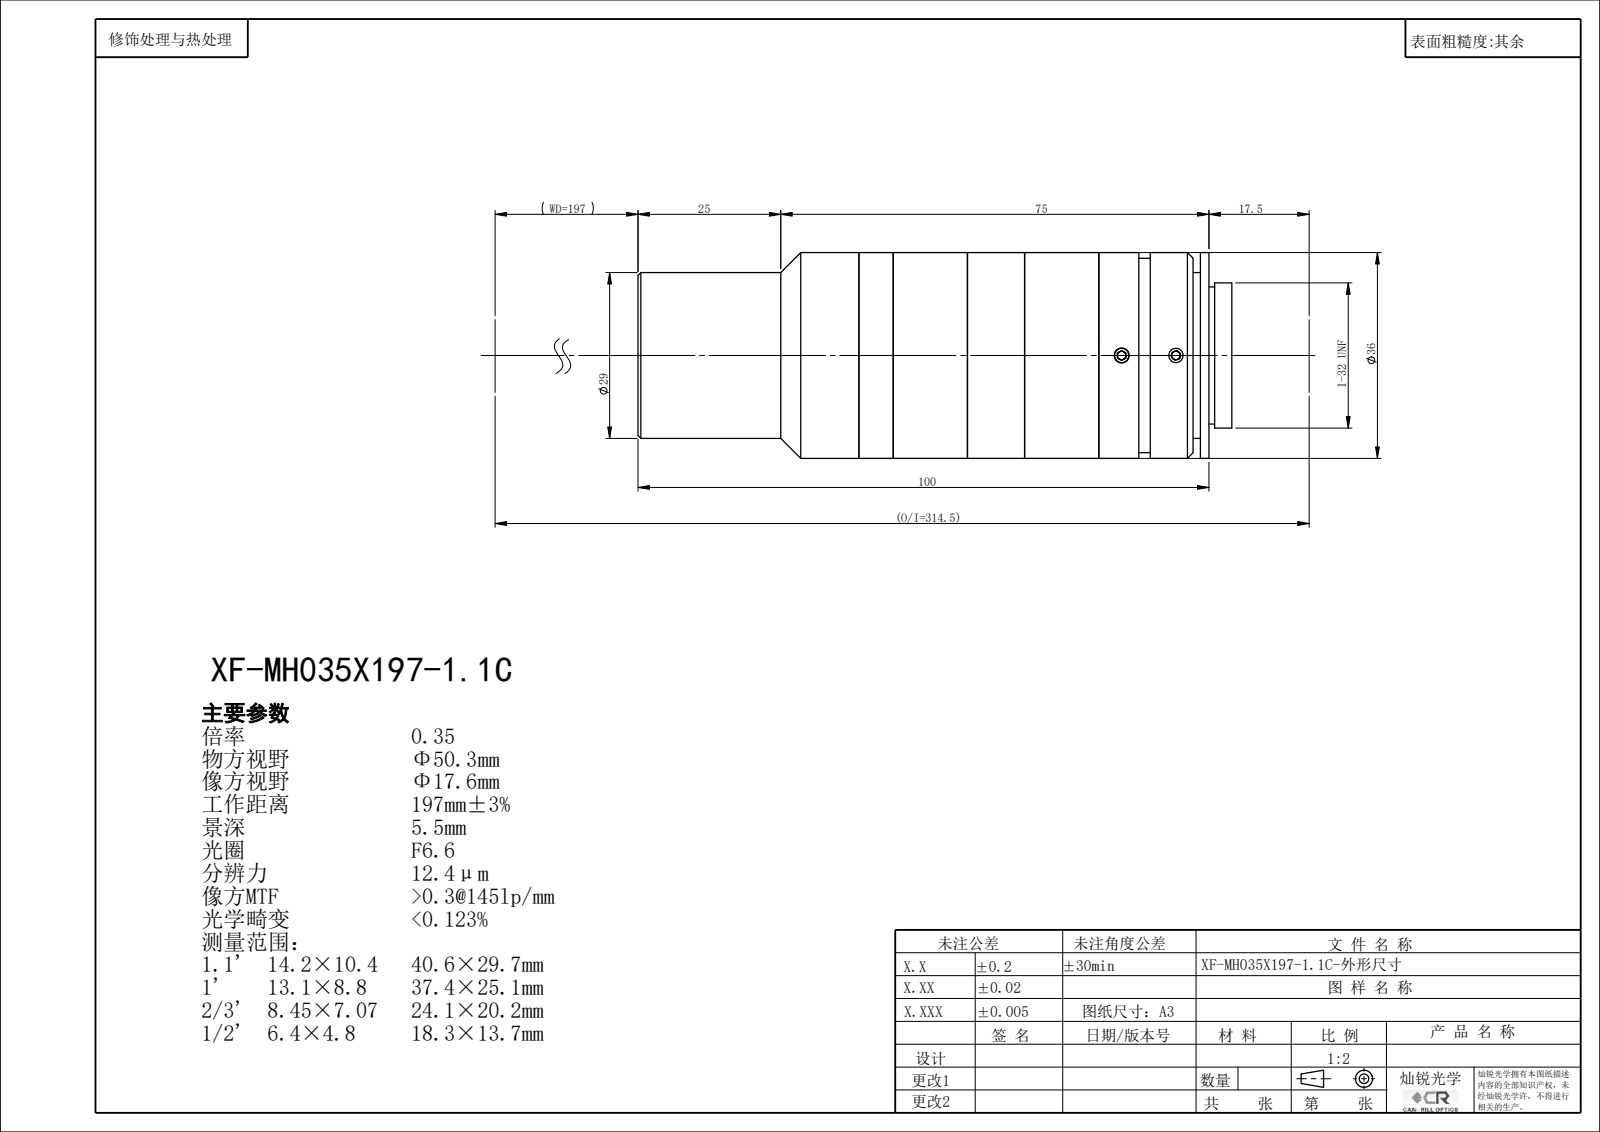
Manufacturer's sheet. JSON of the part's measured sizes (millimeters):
{"part_name": "XF-MH035X197-1.1C", "step_written_by": "SolidWorks 2022 (CONFIG_CONTROL_DESIGN)", "units": "millimeters", "bodies": {"solids": 0, "faces": 146, "planar": 74, "cylindrical": 44, "other": 28}, "overall_size": [103.95, 36, 36], "round_holes": [[2.5, 3], [20, 1], [22.4, 1], [24, 1], [24.9, 1], [26, 1], [26.4, 1]], "round_bosses_or_shafts": [[36, 1], [34, 1], [29, 1], [25.4, 1]], "face_to_face_distances": [19.27, 1.5, 17.77, 13, 23, 30.77, 32.27, 10, 40.77, 42.27]}
